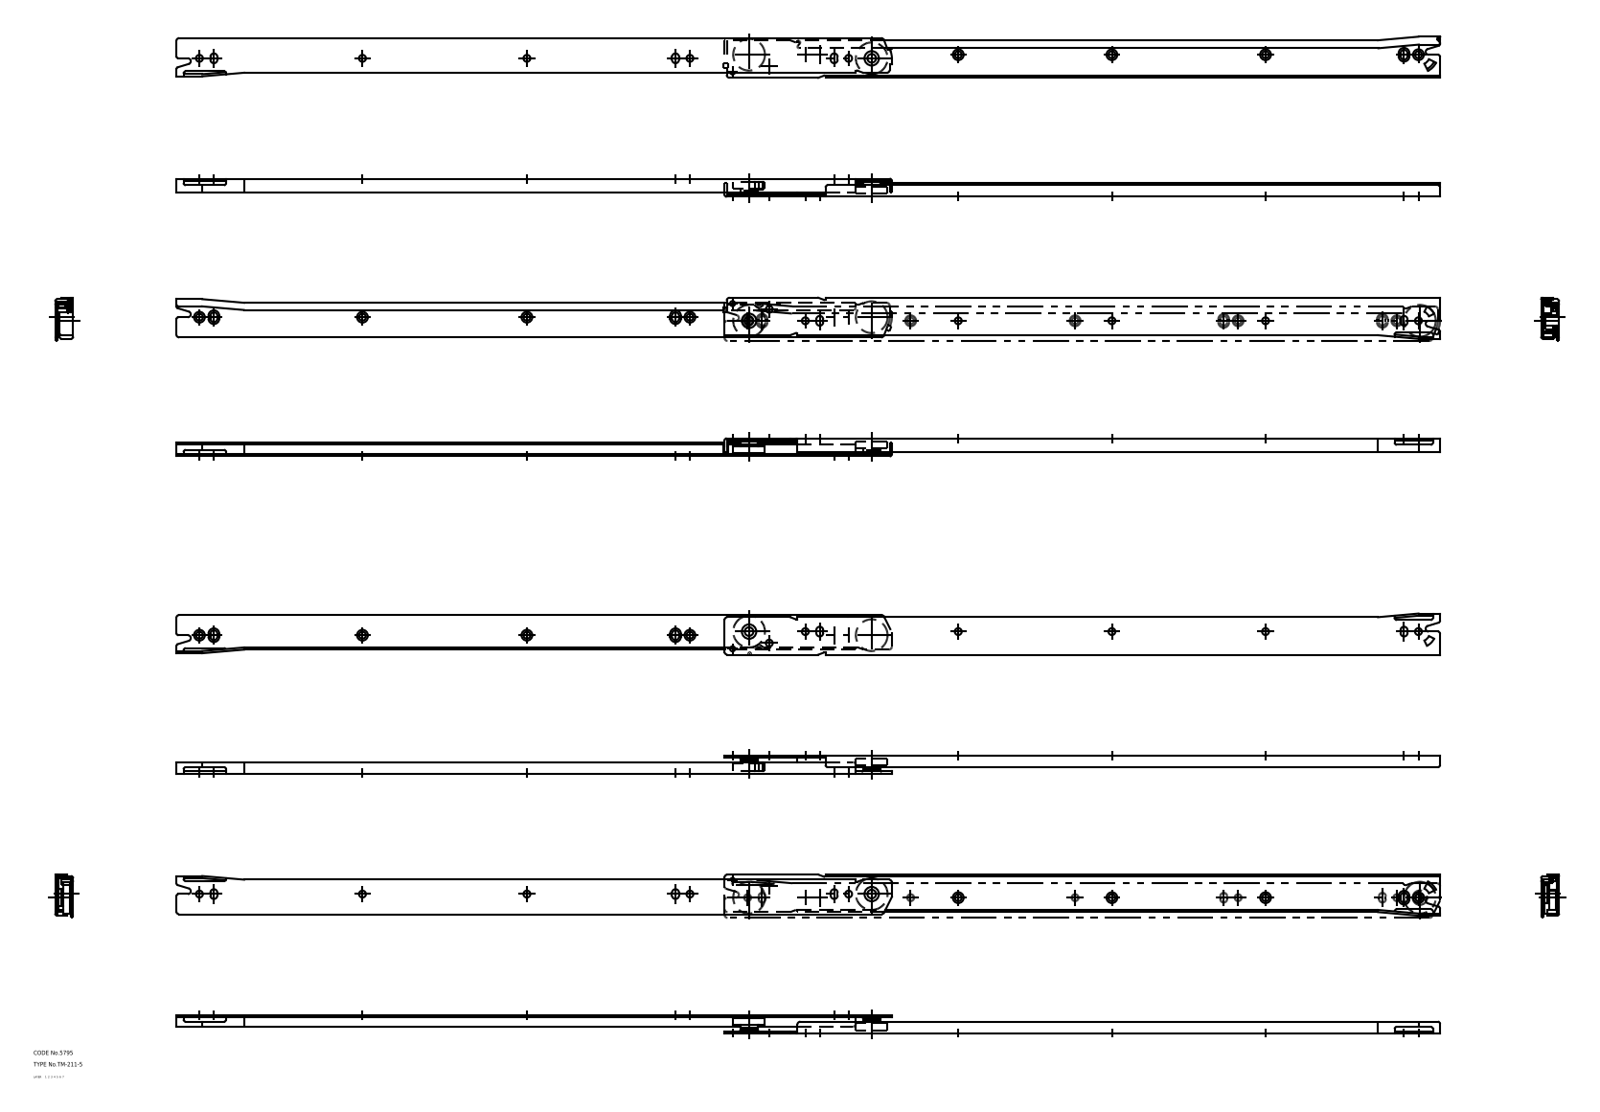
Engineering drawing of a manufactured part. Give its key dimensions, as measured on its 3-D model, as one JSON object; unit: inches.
{"part_name": "roller; member_B; member_A; TM_211_5_1246_36", "step_written_by": "CADfix (AUTOMOTIVE_DESIGN)", "units": "inches", "bodies": {"solids": 4, "faces": 185, "planar": 0, "cylindrical": 0, "other": 185}, "overall_size": [34.488, 1.122, 0.492], "volume_in3": 3.233, "surface_area_in2": 110.4}
